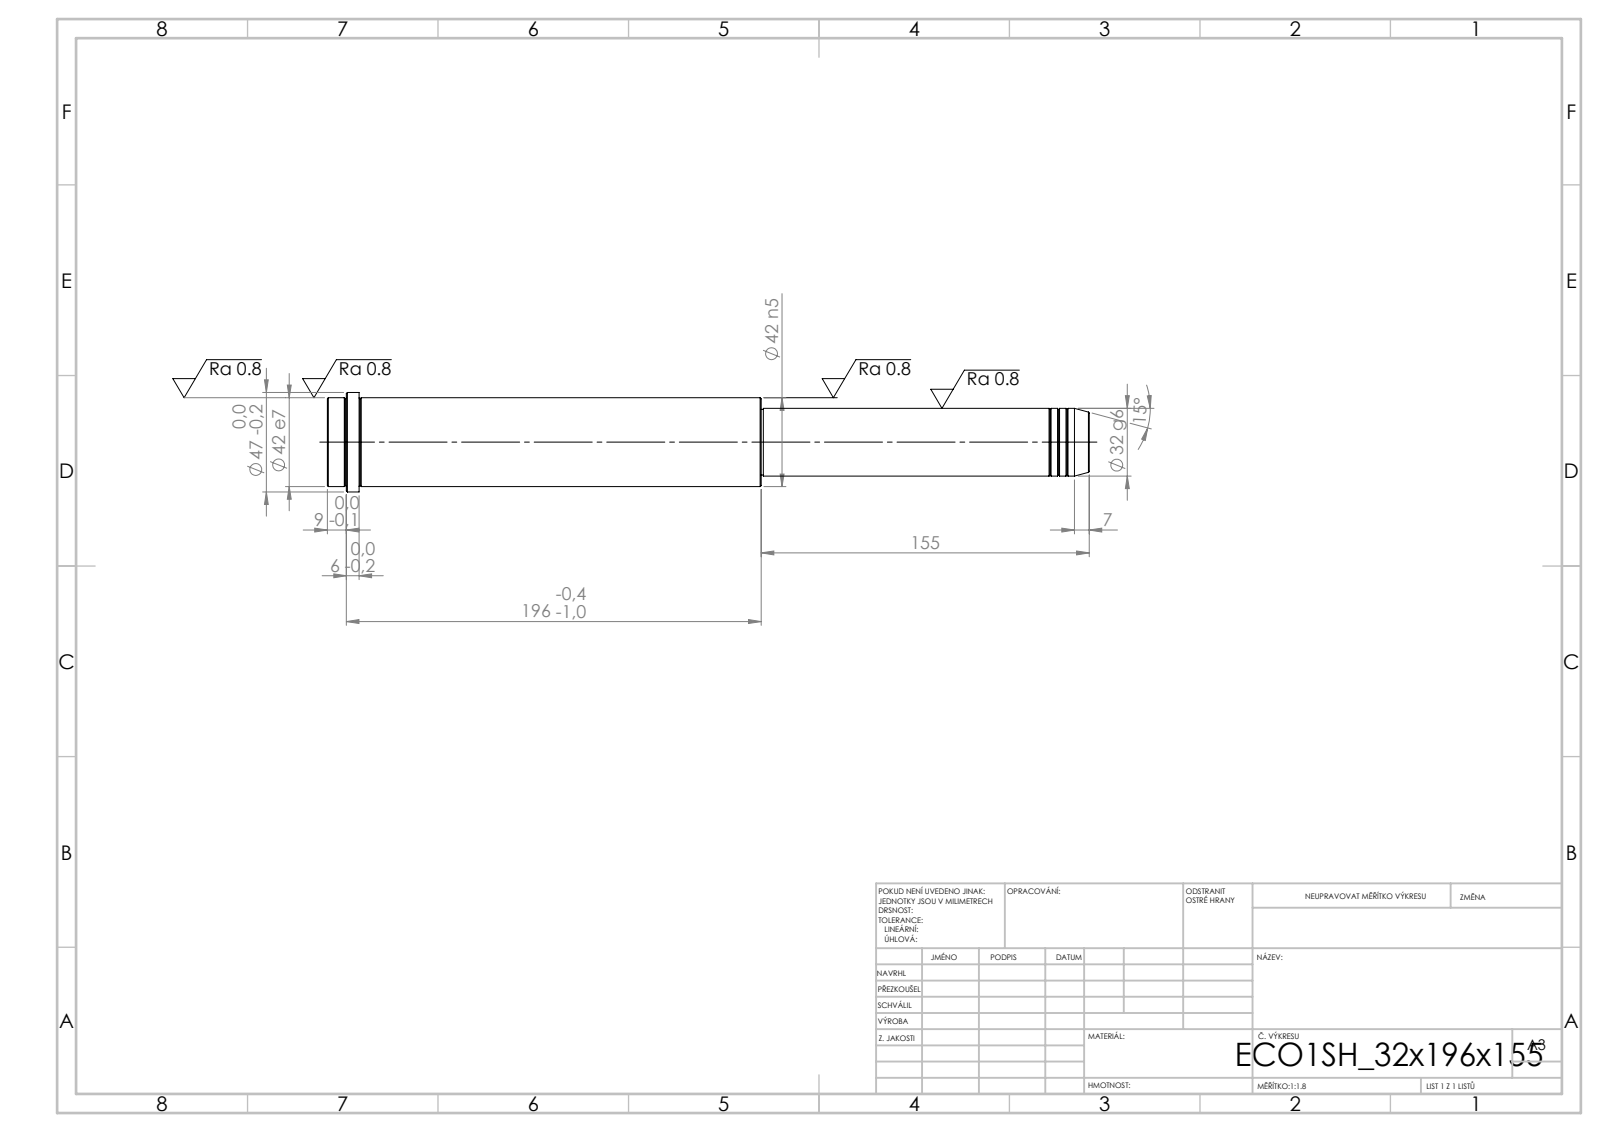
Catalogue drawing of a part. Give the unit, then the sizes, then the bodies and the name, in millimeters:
Units: millimetres
Overall size (bounding box): 360 × 47 × 47
Round bosses / shafts (diameter × count): ⌀47 ×1, ⌀42 ×1, ⌀32 ×1, ⌀31 ×1
Main face-to-face distances: 360, 155, 205, 345, 190, 15, 351, 196, 6, 9
Volume: 409 814 mm³ · Surface area: 46 271 mm²
Bodies: 1 solid, 52 faces (6 planar, 16 cylindrical, 30 other)
STEP written by: SolidWorks 2019 (CONFIG_CONTROL_DESIGN)
